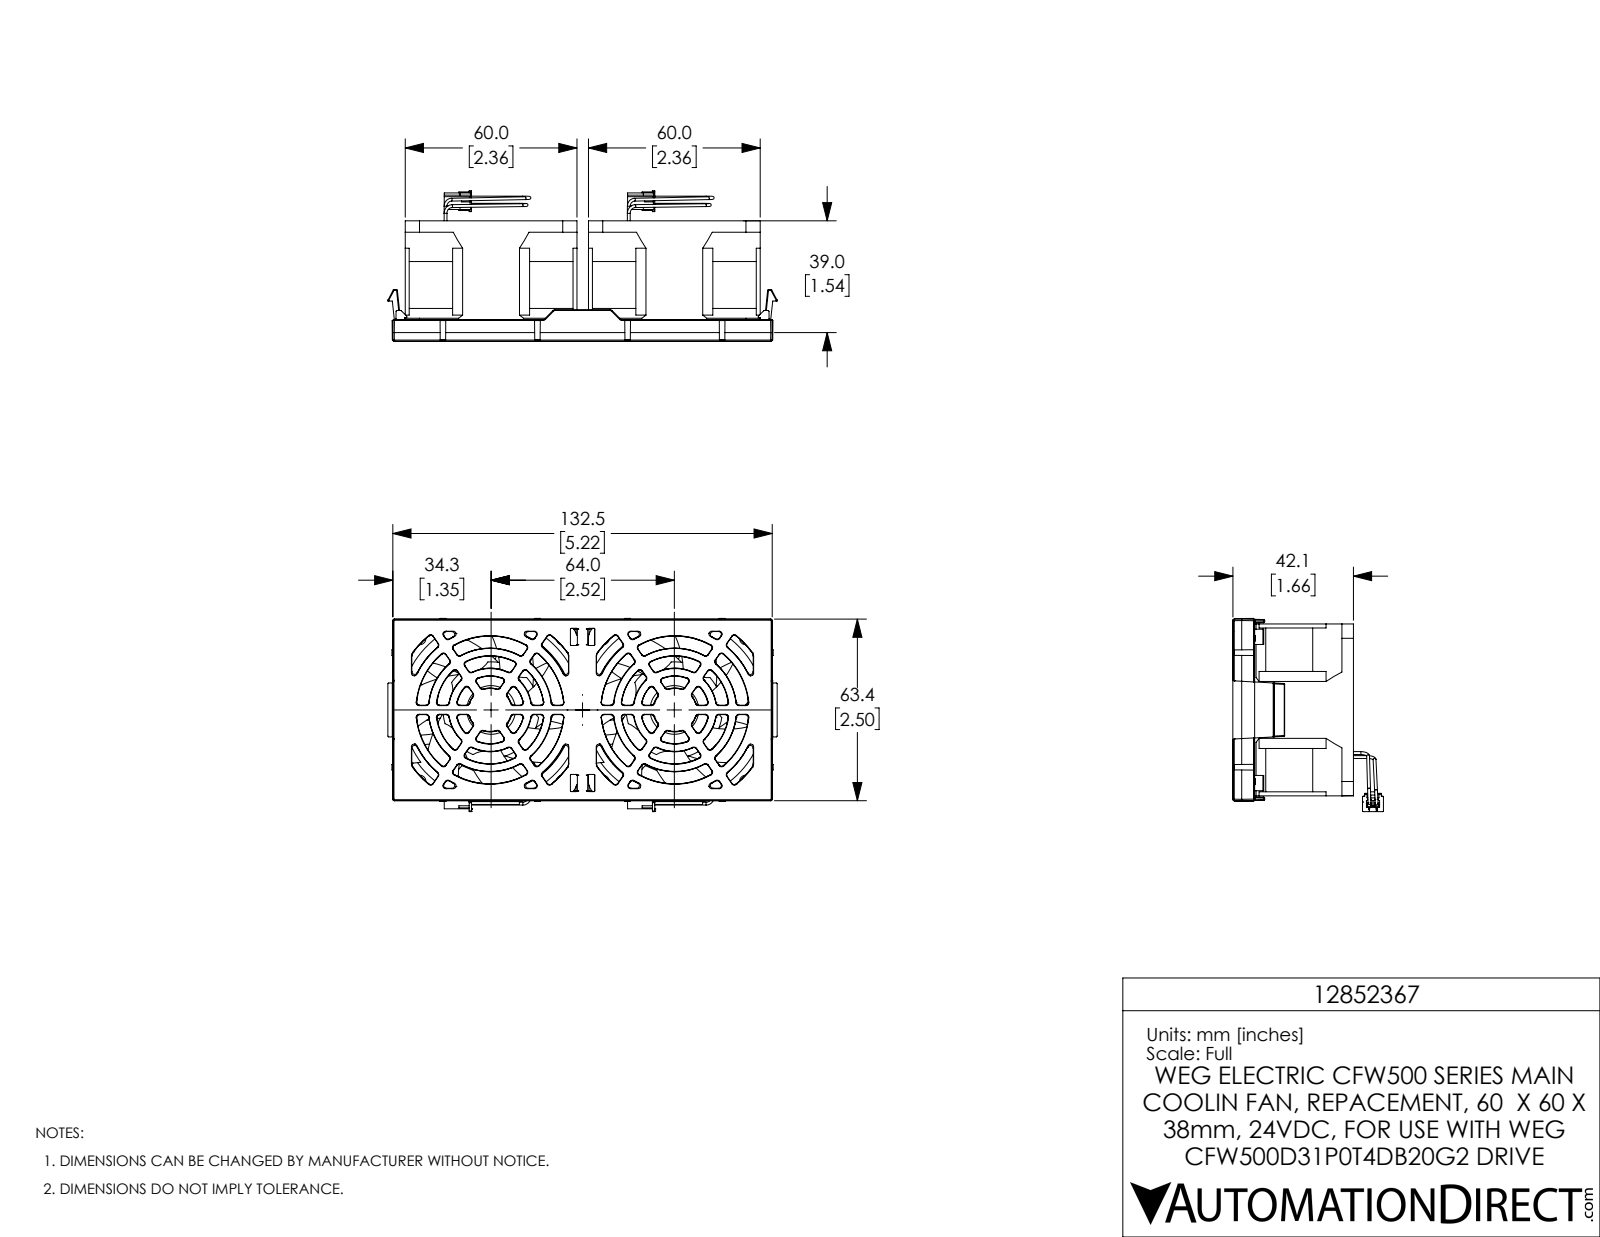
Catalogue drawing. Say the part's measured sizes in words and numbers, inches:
The part is named "10002552384swa000 w ext 3 Grill COMPLETE 1". Its 3-D file was written by "SolidWorks 2017 (AUTOMOTIVE_DESIGN)". It is 11 solids with 3693 faces: 1256 planar, 659 cylindrical and 1778 other. Overall it measures 5.352 by 2.656 by 2.071 inches. Its volume is 7.619 cubic inches and its surface area 141 square inches. Round holes: 8 of diameter 0.177, 2 of diameter 0.669, 2 of diameter 2.252. Round bosses or shafts: 10 of diameter 0.039, 2 of diameter 1.323, 2 of diameter 0.276. Partial cylindrical surfaces (rounded edges, fillets, slot ends): 133 of radius 0.012, 32 of radius 0.02, 16 of radius 0.004, 12 of radius 0.039, 8 of radius 0.197, 8 of radius 1.122, 4 of radius 0.01, 2 of radius 0.02. The main face-to-face distances are 0.137, 2.362, 0.055, 2.307, 2.52, 1.52, 1.657, 0.157, 2.252, 0.079. The hole center spacings are 1.392, 1.969, 2.52, 1.824, 2.784, 3.198, 3.639, 0.551.
